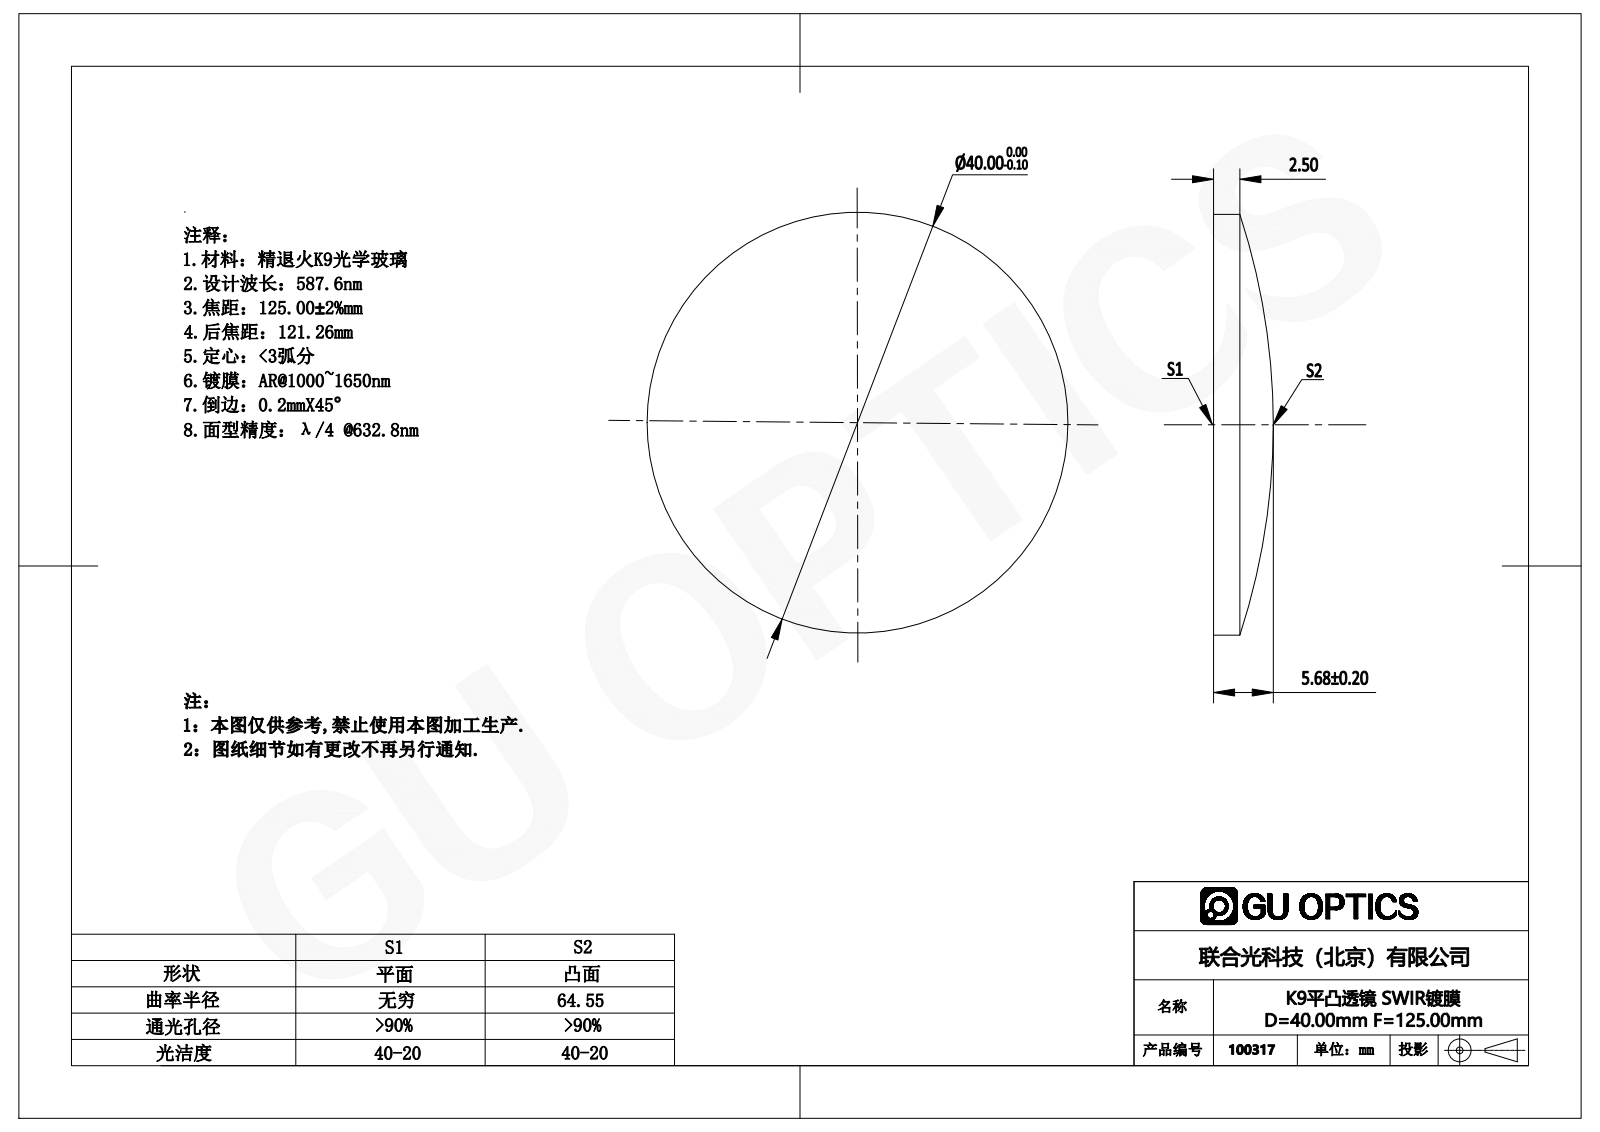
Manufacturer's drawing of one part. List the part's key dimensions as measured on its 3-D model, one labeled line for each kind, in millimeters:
Part name (STEP PRODUCT): 100145
STEP written by: SolidWorks 2016 (AUTOMOTIVE_DESIGN)
Units: millimetres
Bodies: 1 solid, 5 faces (1 planar, 2 cylindrical, 2 other)
Overall size (bounding box): 40 × 40 × 5.68
Volume: 5 156 mm³ · Surface area: 2 859 mm²
Round bosses / shafts (diameter × count): ⌀40 ×1
